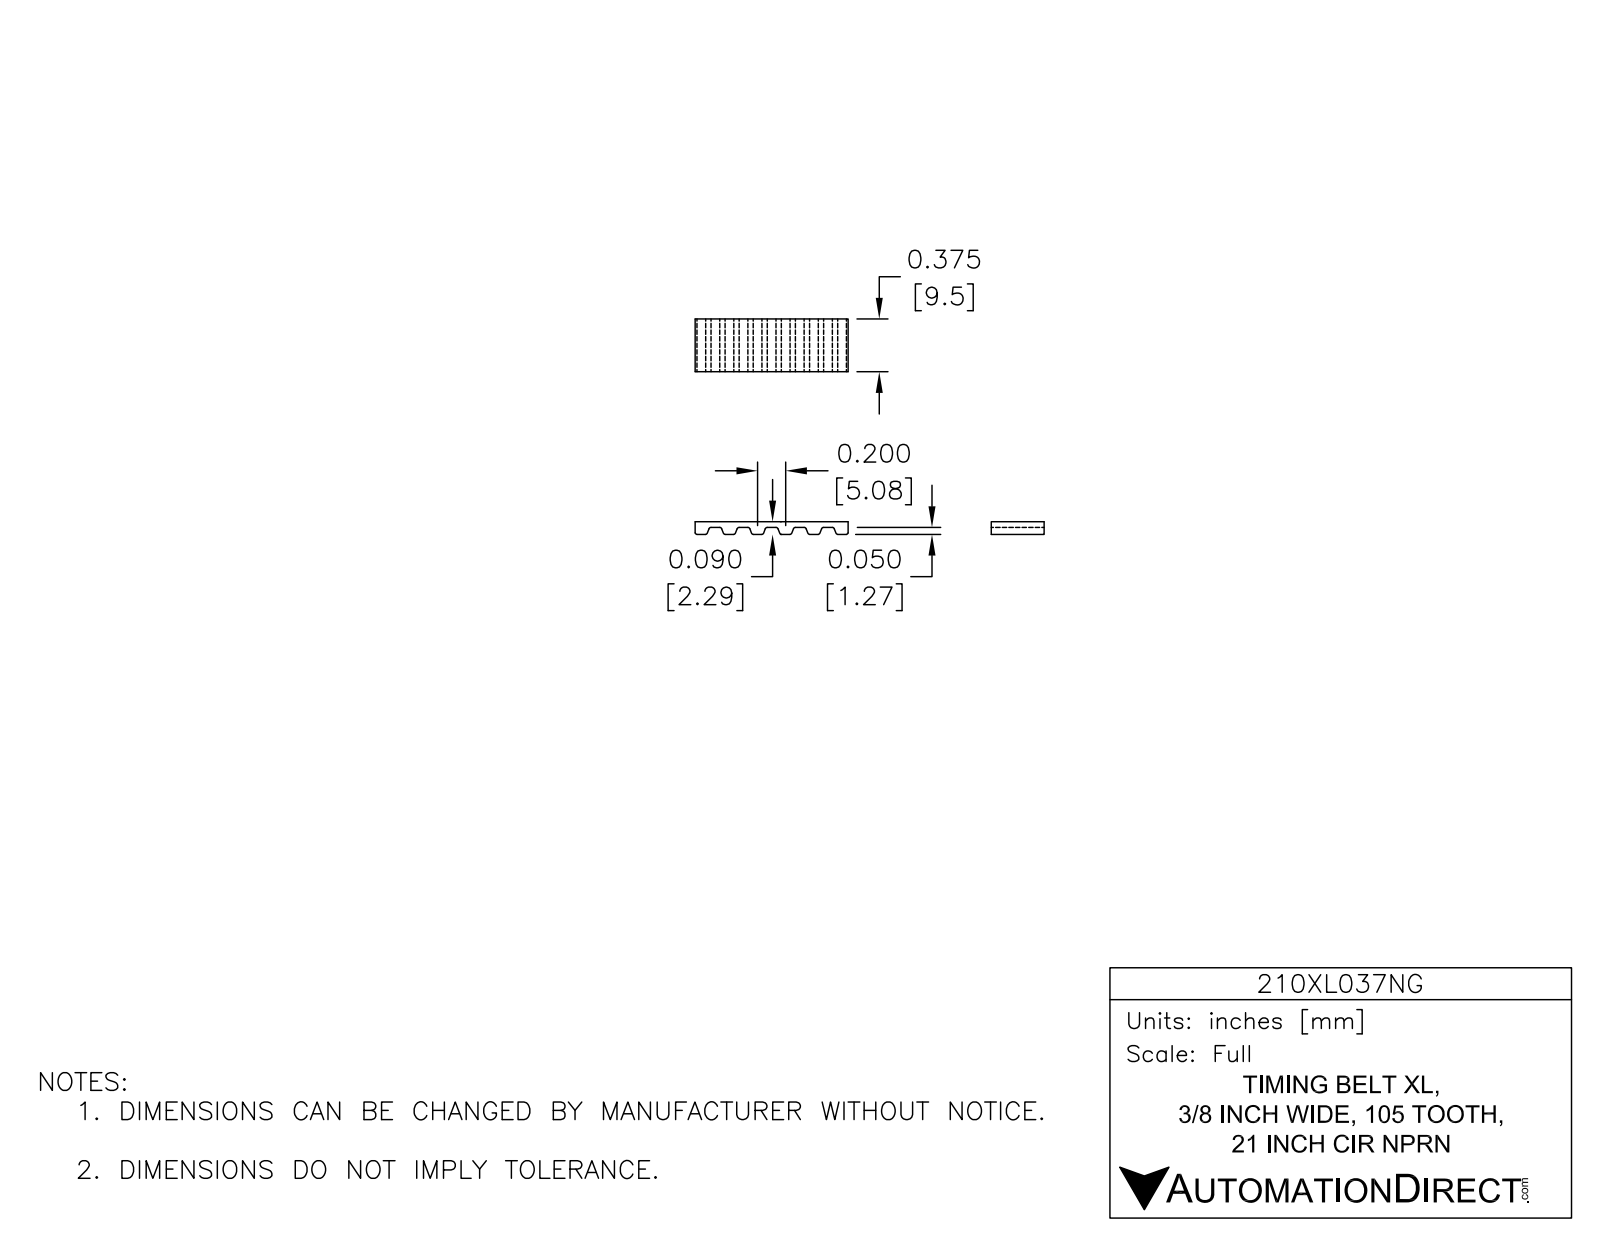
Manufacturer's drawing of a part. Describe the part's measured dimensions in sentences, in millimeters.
The part is named "210XL037NG". Its 3-D file was written by "SolidWorks 2014 (AUTOMOTIVE_DESIGN)". It is 1 solid with 879 faces: 378 planar, 501 cylindrical and 0 other. Overall it measures 223.2 by 76.2 by 9.5 millimeters. Its volume is 7 010 cubic millimeters and its surface area 12 970 square millimeters. Partial cylindrical surfaces (rounded edges, fillets, slot ends): 420 of radius 0.4, 2 of radius 37.1, 2 of radius 38.1. The main face-to-face distances are 76.2, 1, 75.2, 9.5, 74.2, 2.3, 73.9, 1.3, 72.9, 4.5.
